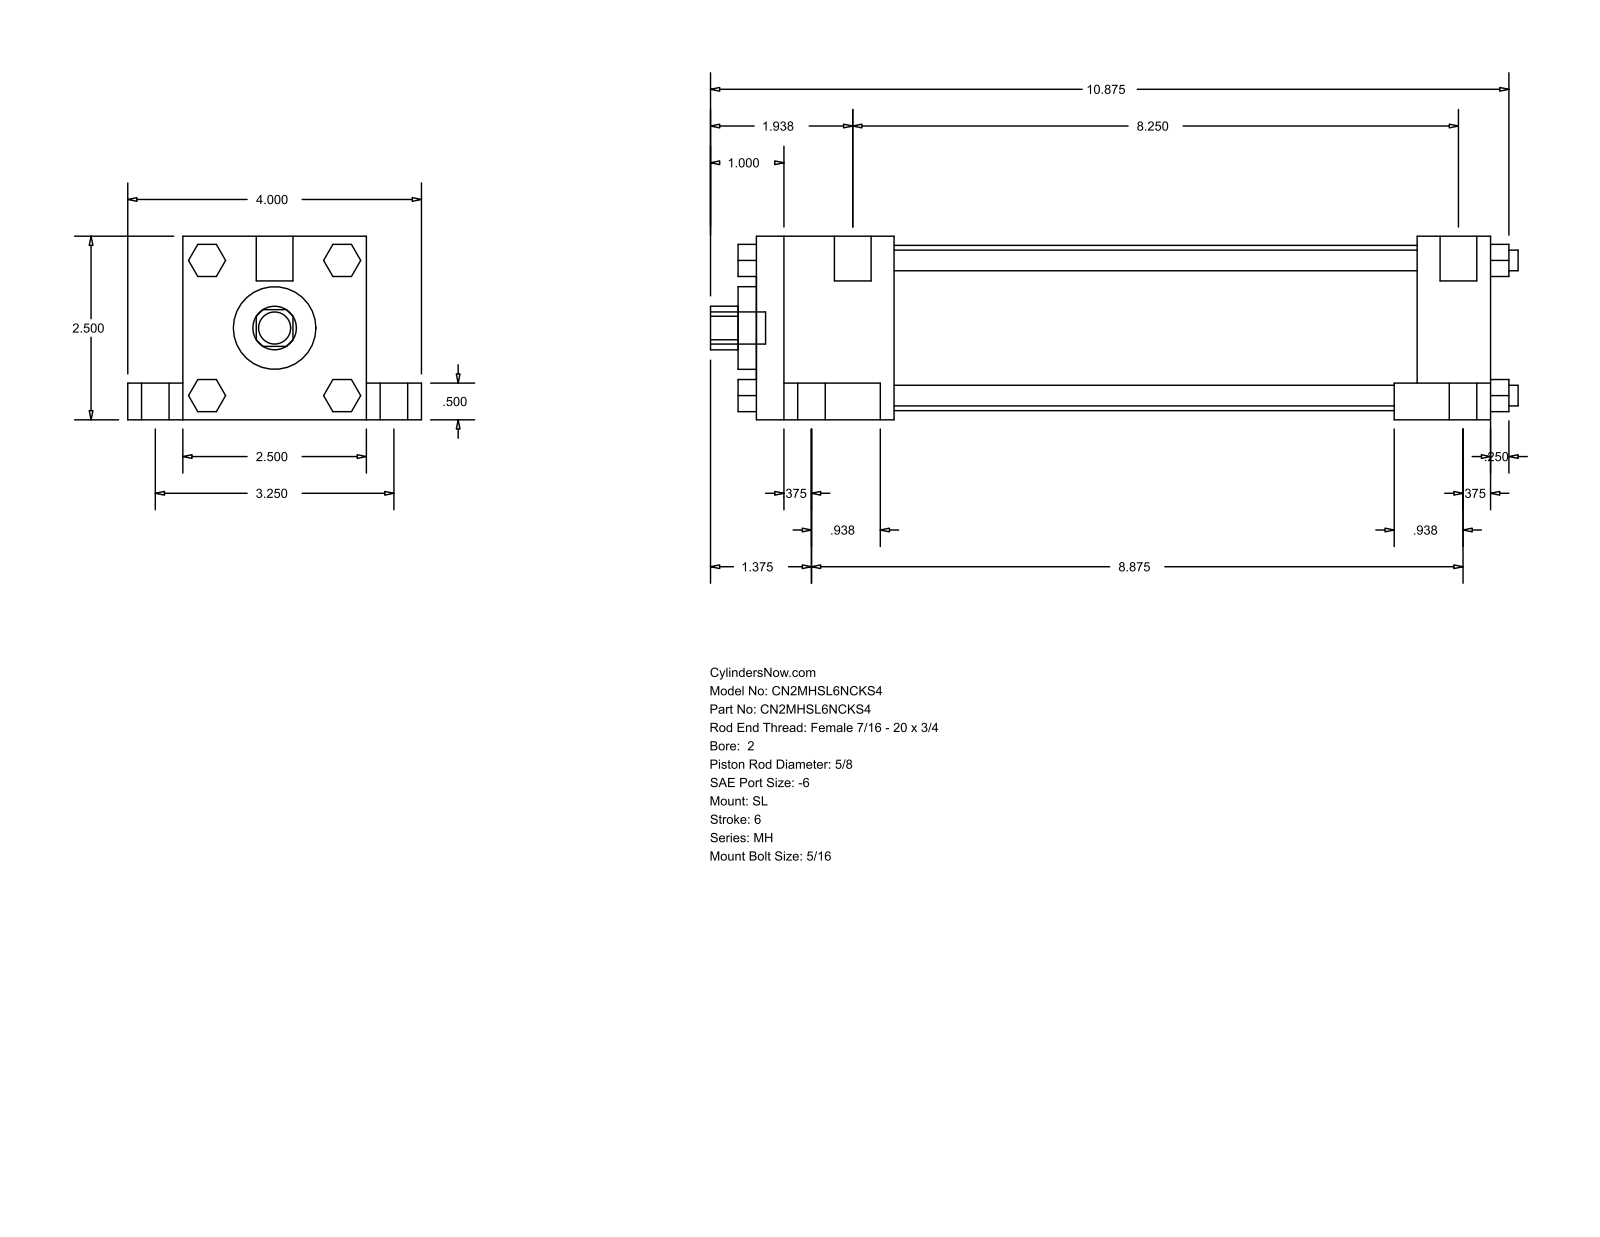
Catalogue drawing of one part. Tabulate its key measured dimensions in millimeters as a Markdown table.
| quantity | value |
| --- | --- |
| part name | MH_SL__0200_0.625 |
| STEP written by | GSSL Pune (CONFIG_CONTROL_DESIGN) |
| units | millimeters |
| bodies | 0 solids, 148 faces (112 planar, 36 cylindrical, 0 other) |
| overall size | 279.4 × 101.6 × 63.5 |
| round holes (diameter × count) | 15.88 × 1, 28.57 × 1, 57.15 × 1 |
| round bosses / shafts (diameter × count) | 15.88 × 4, 9.53 × 4, 7.14 × 4, 5.56 × 4, 12.7 × 2, 11.11 × 1 |
| partial cylindrical surfaces (radius × count) | 7.54 × 1 |
| main face-to-face distances | 63.5, 254, 12.7, 19.05, 50.8, 82.55, 228.59, 25.41, 47.62, 180.97 |
